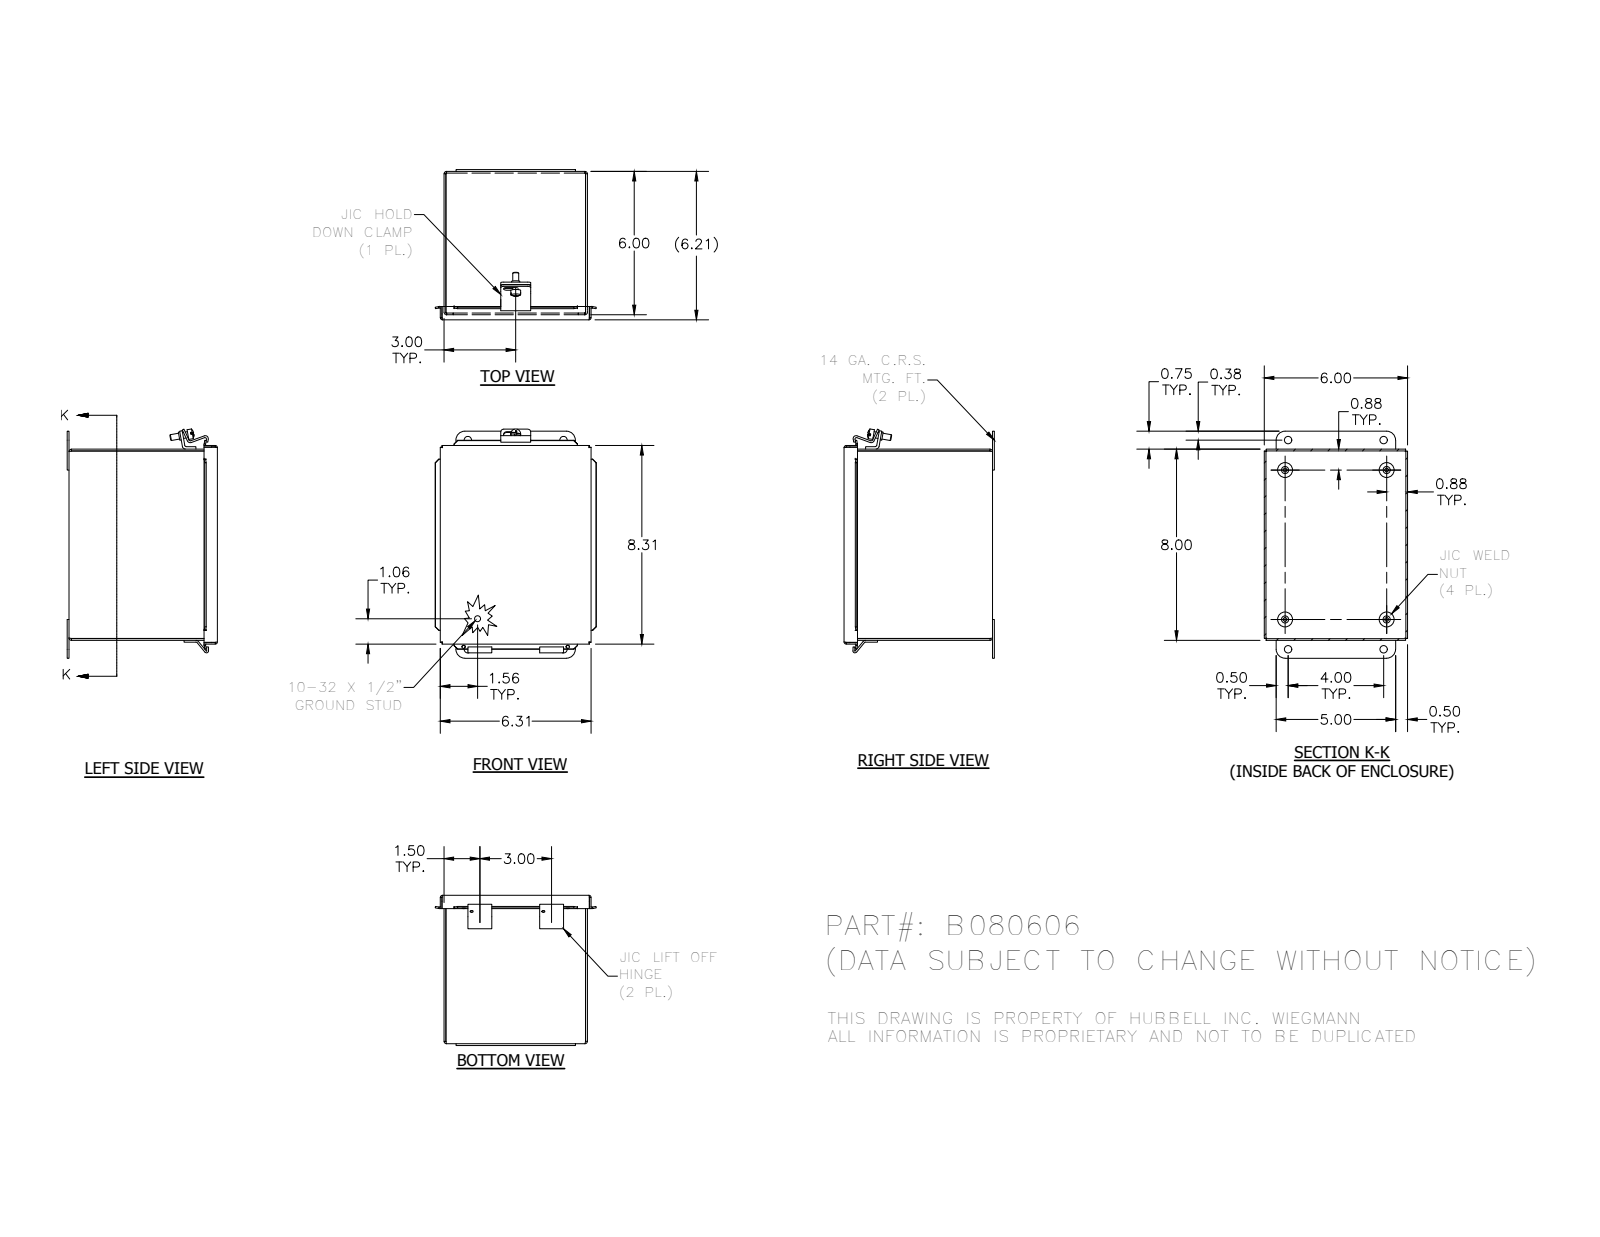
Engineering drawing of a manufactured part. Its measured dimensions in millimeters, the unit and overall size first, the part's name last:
Units: millimetres
Overall size (bounding box): 243.7 × 171.2 × 159.7
Round holes (diameter × count): ⌀4 ×4, ⌀7.9 ×4, ⌀3.2 ×2, ⌀3.6 ×2, ⌀5 ×1
Round bosses / shafts (diameter × count): ⌀15.9 ×4, ⌀7.6 ×4, ⌀6.4 ×2, ⌀10.4 ×1, ⌀8.7 ×1, ⌀4.8 ×1
Partial cylindrical surfaces — rounded edges, fillets, slot ends (radius × count): R0.8 ×16, R2.4 ×8, R2.7 ×8, R3.2 ×4, R9.5 ×4, R1.6 ×3, R3.2 ×3, R3.4 ×2
Main face-to-face distances: 1.9, 150.5, 201.3, 156.2, 152.4, 148.6, 1.6, 157.8, 154.3, 155.9
Hole centre spacings: 31.9, 190.5, 217.4, 101.6, 108, 109.5, 109.5, 158.8
Volume: 416 700 mm³ · Surface area: 438 500 mm²
Bodies: 16 solids, 369 faces (245 planar, 82 cylindrical, 42 other)
Part name (STEP PRODUCT): B080606; 3499; 3482; C1001 (+7 more)
STEP written by: Autodesk Inventor 2012 (AUTOMOTIVE_DESIGN)
